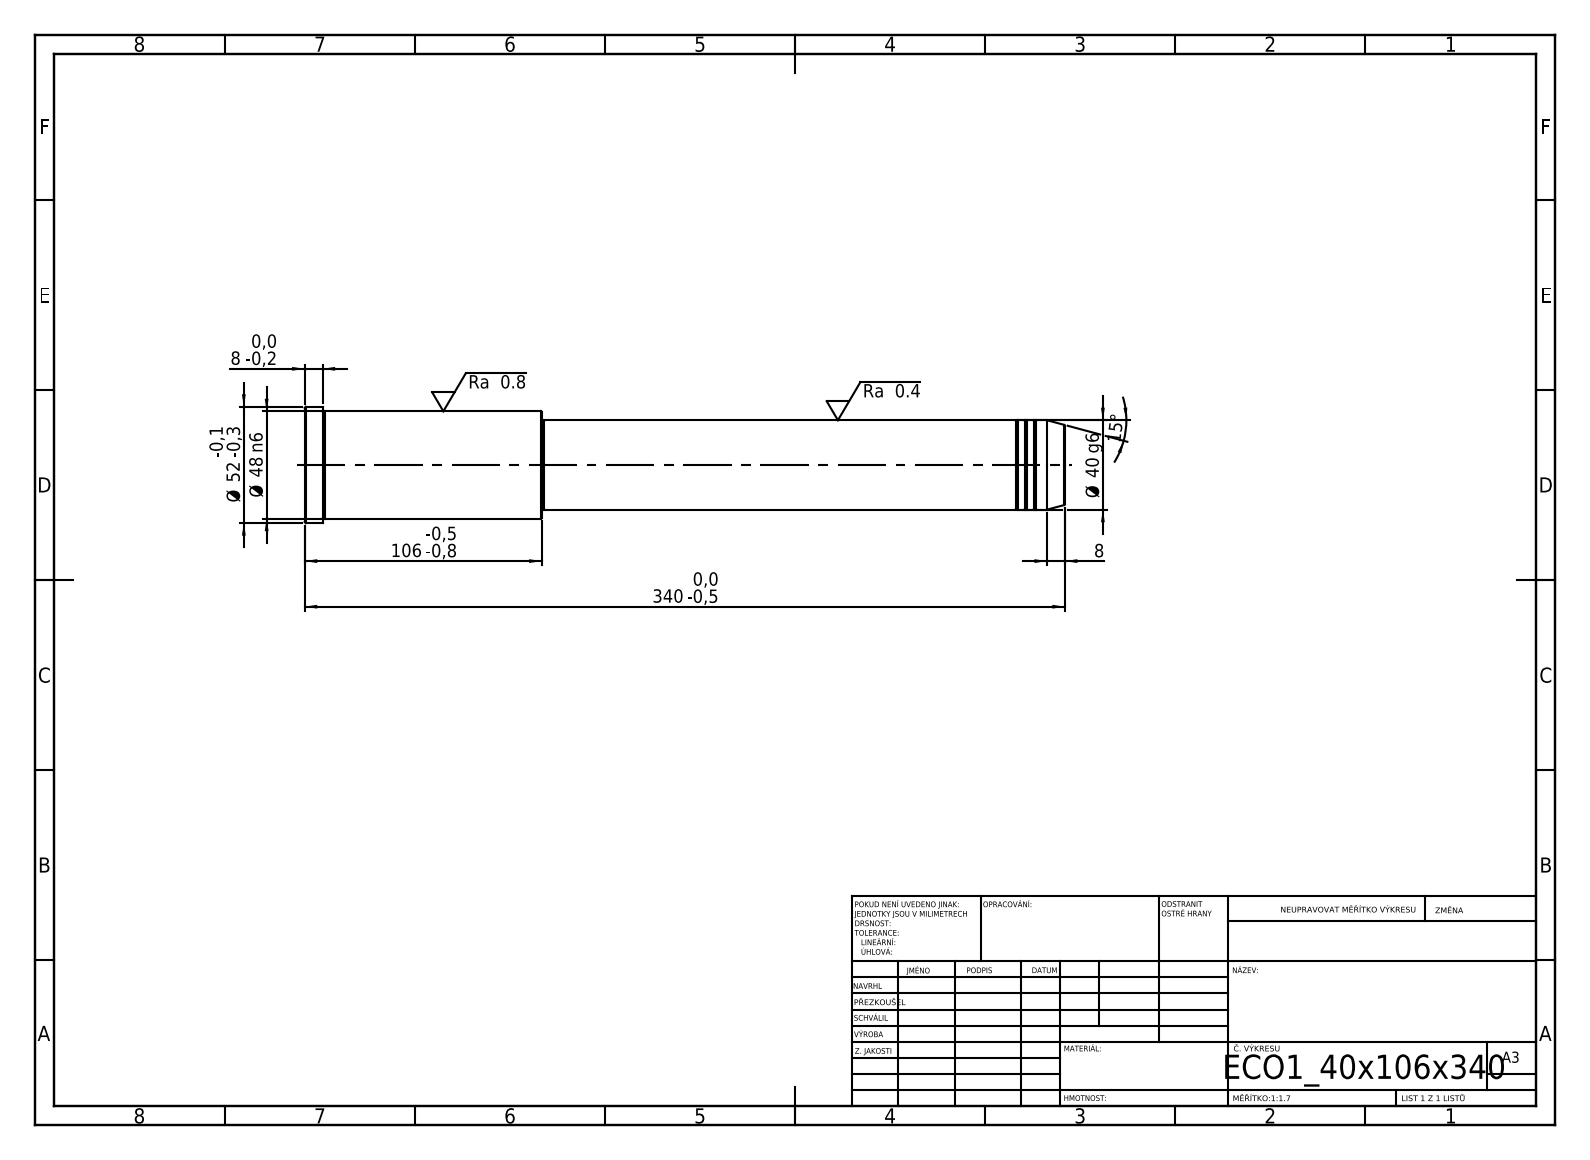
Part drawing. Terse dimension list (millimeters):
written by: SolidWorks 2019 (CONFIG_CONTROL_DESIGN)
unit: mm
bodies: 1 solid, 43 faces (5 planar, 14 cylindrical, 24 other)
size: 340 × 52 × 52
volume: 487 031 mm³; area: 49 767 mm²
bosses: 1× ⌀52, 1× ⌀48, 1× ⌀40, 1× ⌀39
face distances: 340, 234, 106, 332, 98, 8, 233, 1, 99, 107
